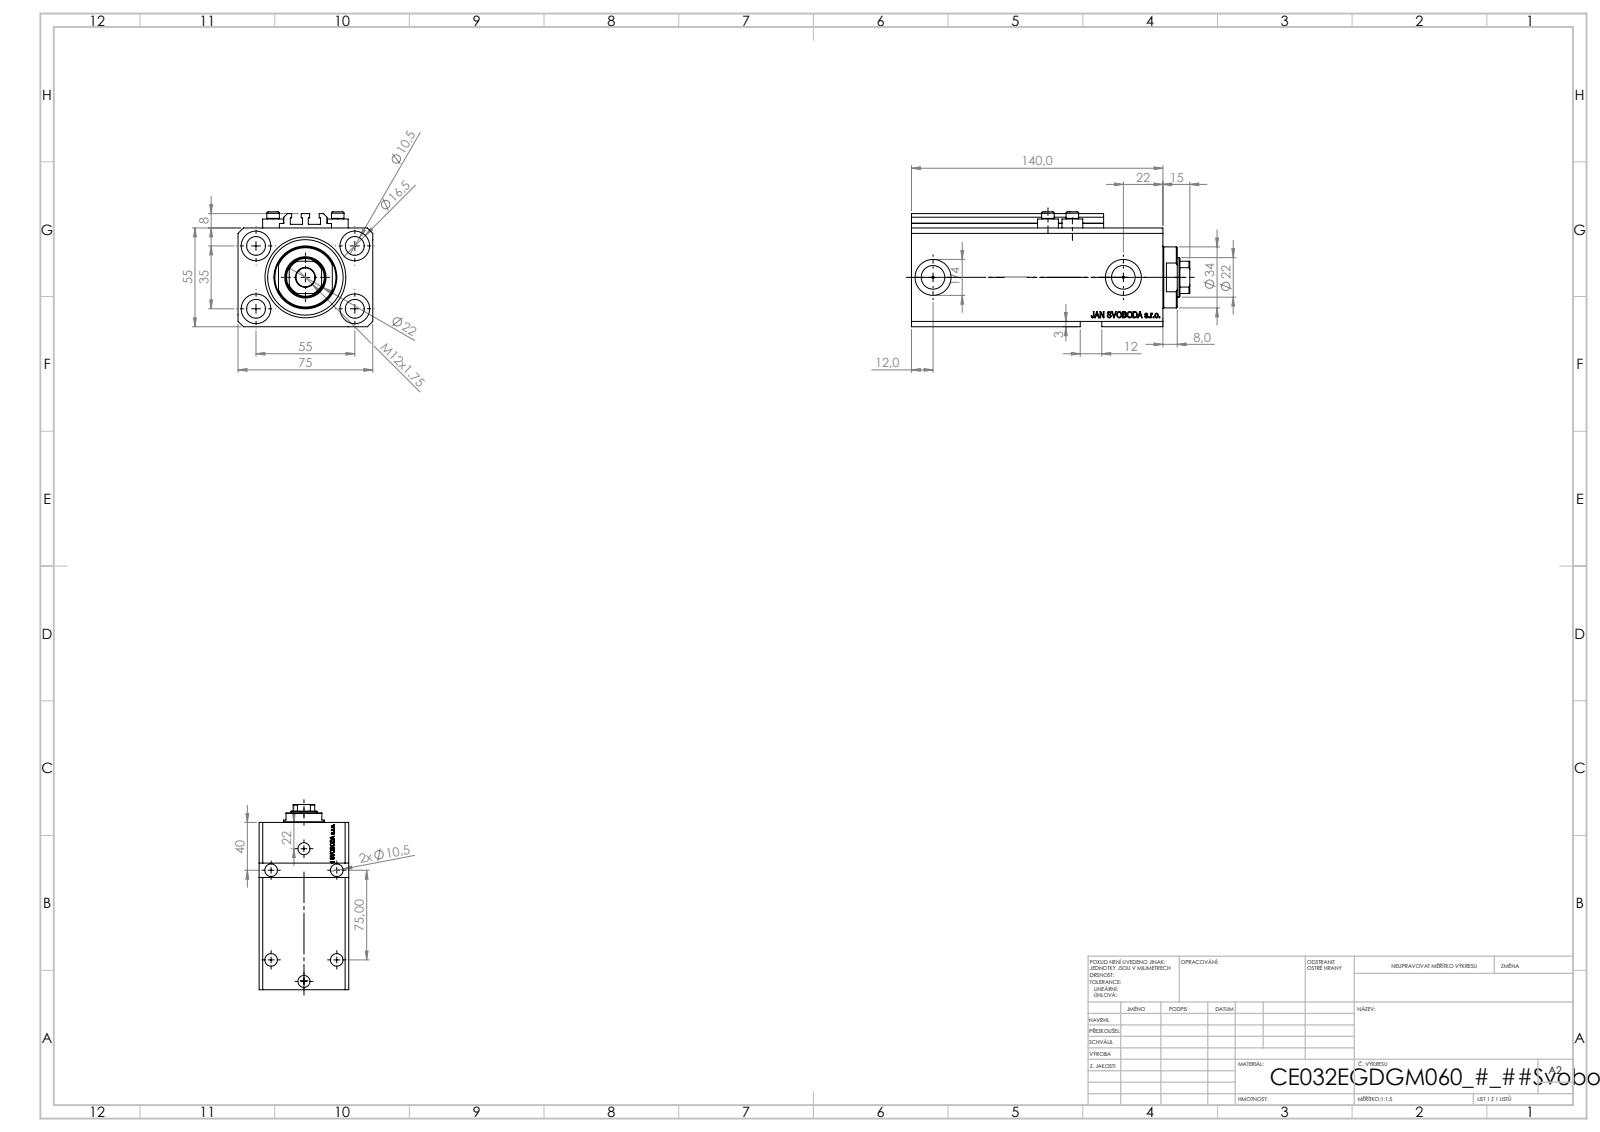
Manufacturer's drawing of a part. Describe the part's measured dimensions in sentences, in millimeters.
The part is named "V250CE_E_Body; V250CE_C_VCP; ALLEN BOLT V250CE; V250CE_VC_E". Its 3-D file was written by "SolidWorks 2019 (CONFIG_CONTROL_DESIGN)". It is 8 solids with 1100 faces: 518 planar, 158 cylindrical and 424 other. Overall it measures 155 by 75 by 64 millimeters. Its volume is 481 599 cubic millimeters and its surface area 116 451 square millimeters. Round holes: 9 of diameter 10.5, 4 of diameter 1.25, 4 of diameter 4, 4 of diameter 16.5, 2 of diameter 10, 2 of diameter 13.16, 2 of diameter 20, 1 of diameter 22, 1 of diameter 32, 1 of diameter 45. Round bosses or shafts: 4 of diameter 11.6, 4 of diameter 7, 1 of diameter 34. Partial cylindrical surfaces (rounded edges, fillets, slot ends): 10 of radius 0.2, 1 of radius 10.5. The main face-to-face distances are 55, 75, 15, 9.9, 140, 125, 3, 57, 115.1, 130.1. The hole center spacings are 32.6, 32.87, 55, 96.98, 13.6, 14.09, 25.81, 32.58.
